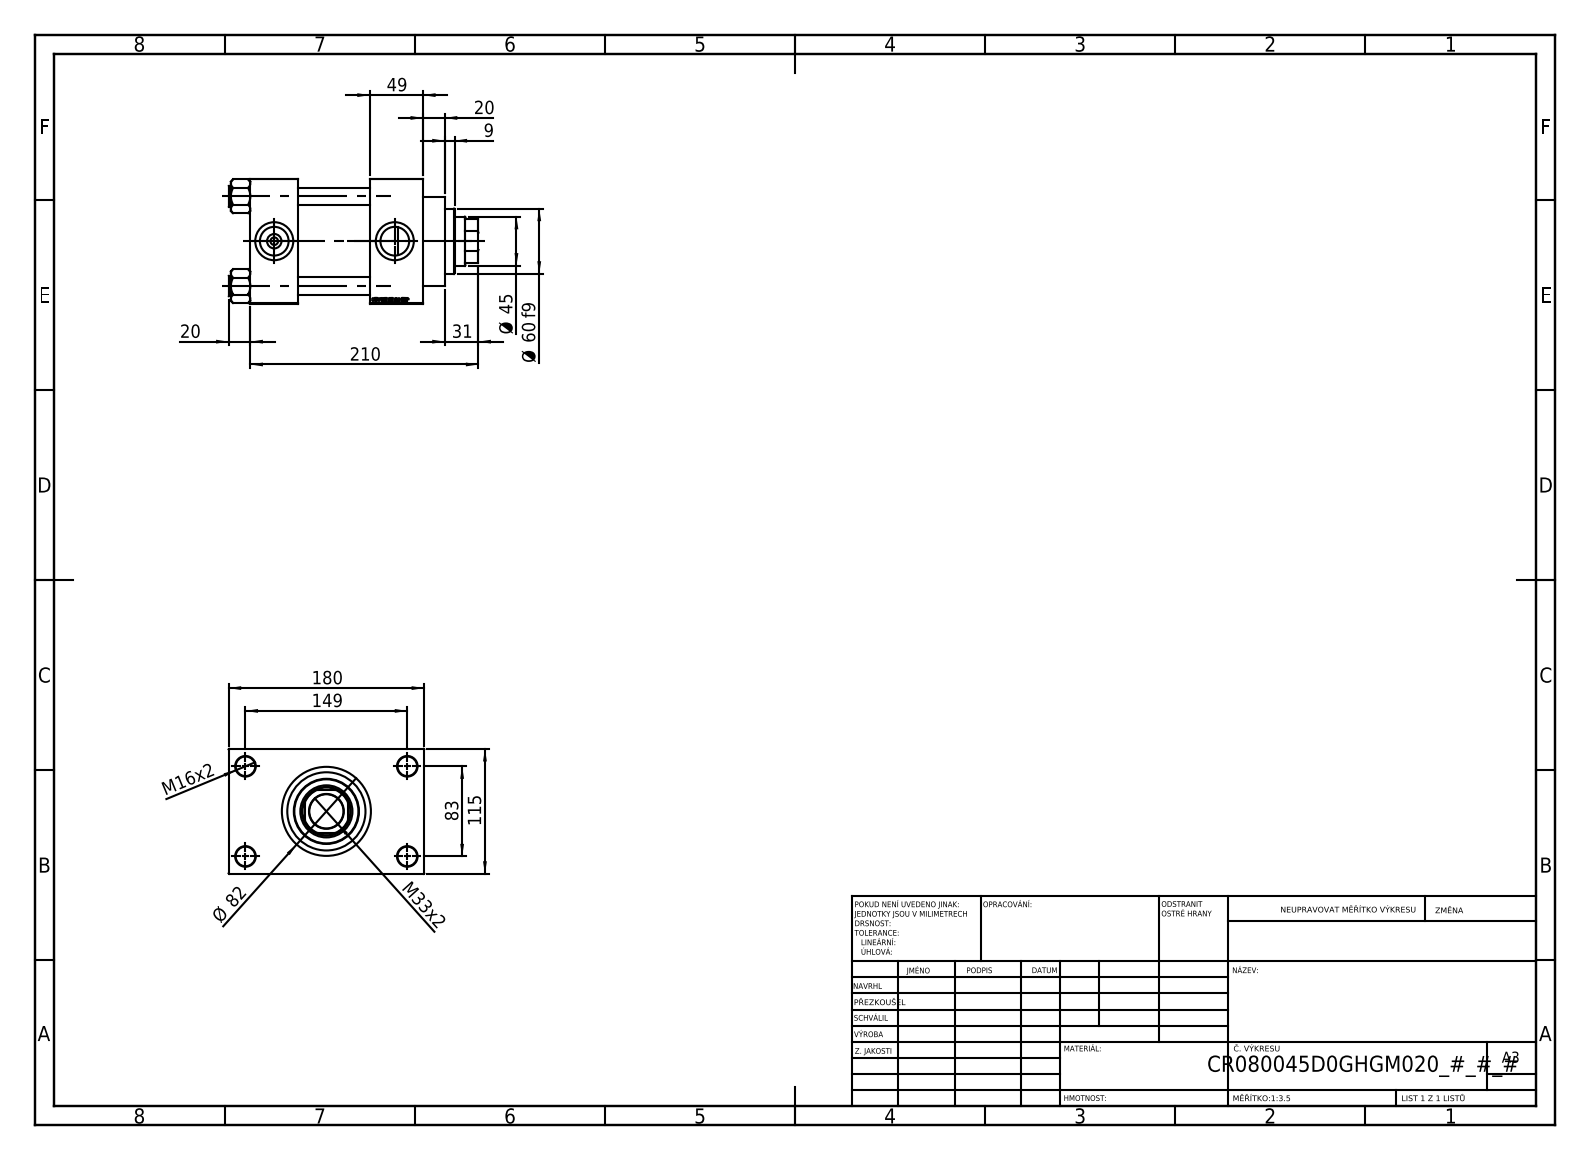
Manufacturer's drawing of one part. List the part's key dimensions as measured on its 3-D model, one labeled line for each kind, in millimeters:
Part name (STEP PRODUCT): NUT_M5_D; V215CR_VCP_D; V215_VC_A; V215CR_D_Body (+1 more)
STEP written by: SolidWorks 2019 (CONFIG_CONTROL_DESIGN)
Units: millimetres
Bodies: 11 solids, 1151 faces (545 planar, 88 cylindrical, 518 other)
Overall size (bounding box): 230 × 180 × 115
Volume: 2 004 000 mm³ · Surface area: 302 449 mm²
Round holes (diameter × count): ⌀16 ×4, ⌀18 ×4, ⌀7 ×2, ⌀26.44 ×2, ⌀35 ×2, ⌀31.5 ×1, ⌀45 ×1, ⌀48 ×1, ⌀61 ×1, ⌀72 ×1, ⌀80 ×1
Round bosses / shafts (diameter × count): ⌀19 ×4, ⌀86 ×1, ⌀82 ×1, ⌀60 ×1
Partial cylindrical surfaces — rounded edges, fillets, slot ends (radius × count): R22 ×1
Main face-to-face distances: 115, 110, 66, 49, 44, 159, 32.5, 147.5, 20, 69
Hole centre spacings: 33.15, 58.48, 82.7, 85.28, 89.24, 115.85, 142.43, 83
